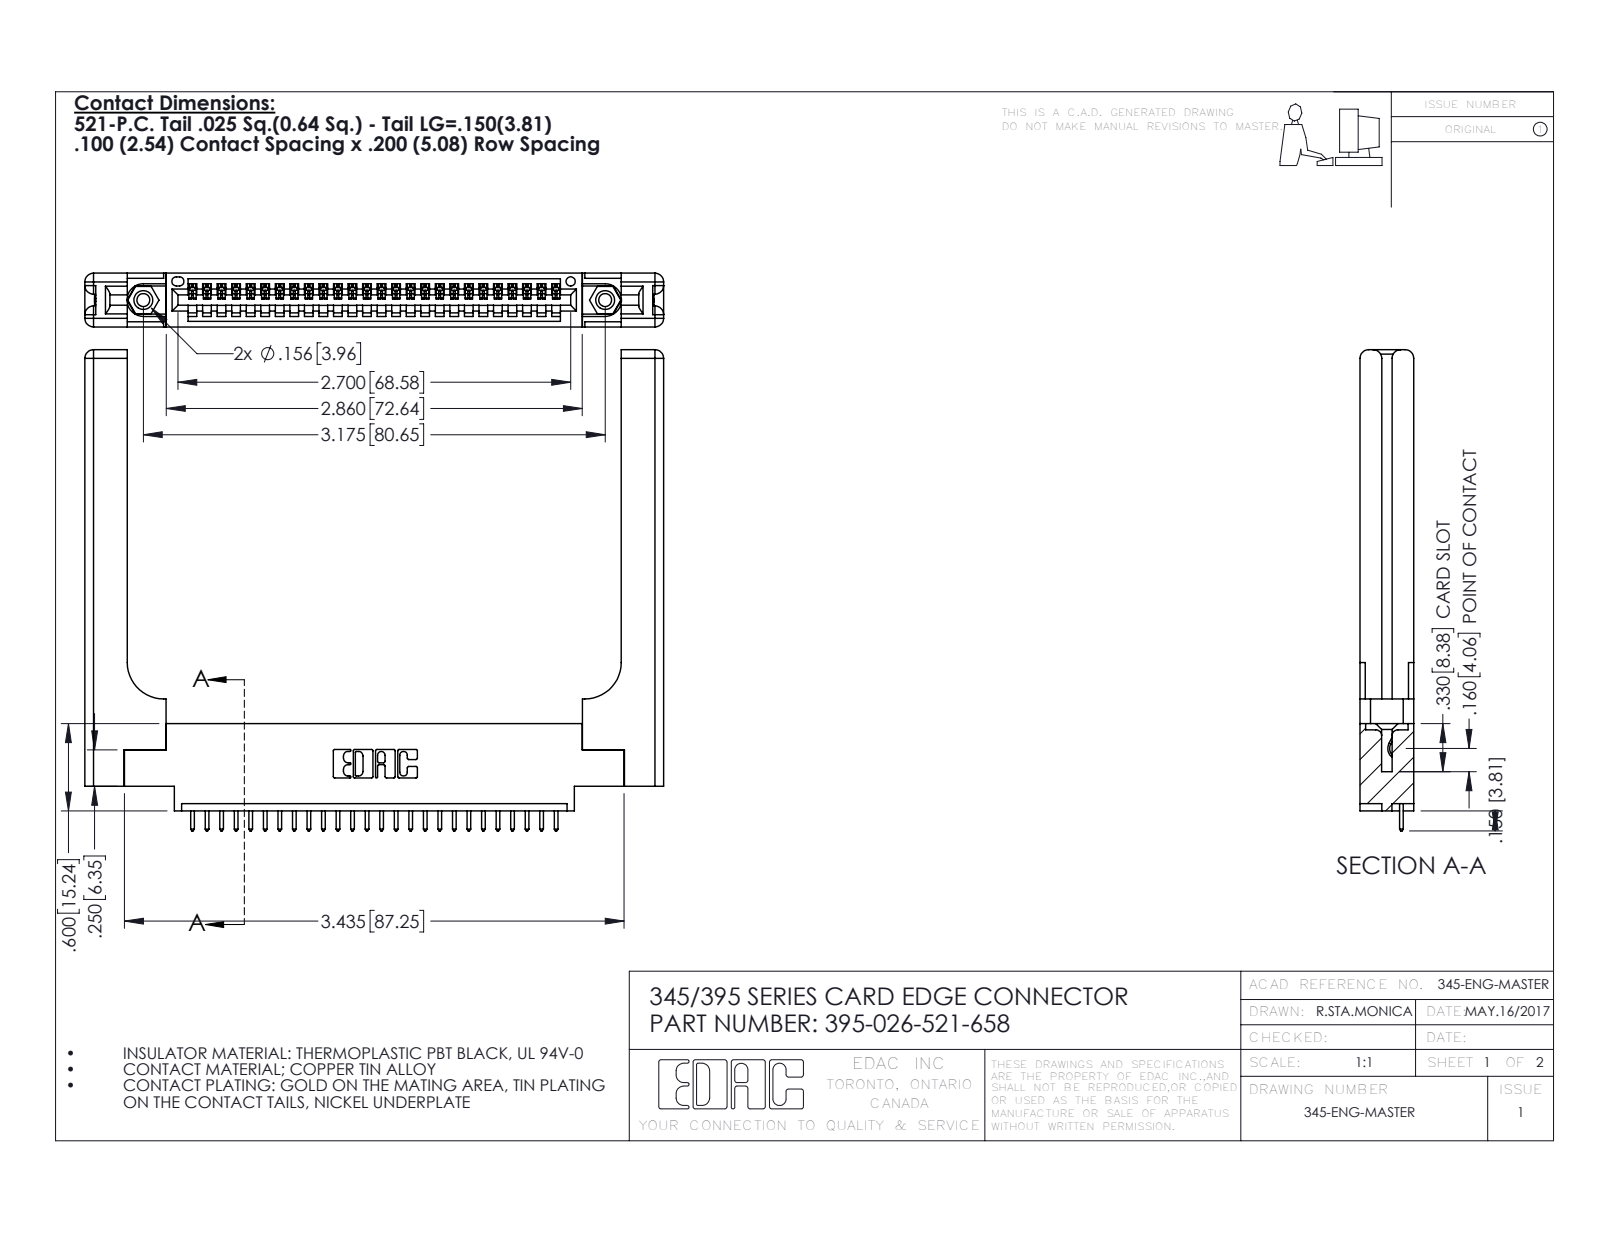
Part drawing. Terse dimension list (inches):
name: 345 Part_0.170 Offset - 0.156 Dia-TH; 345-220-058_345-220-058; 345-250-001_345-250-001-102; 395-026-521-658 (+1 more)
written by: SolidWorks 2016 (CONFIG_CONTROL_DESIGN)
unit: in
bodies: 31 solids, 1894 faces (1272 planar, 562 cylindrical, 60 other)
size: 3.979 × 3.307 × 0.37
volume: 1.085 in³; area: 26.75 in²
holes: 2× ⌀0.089, 2× ⌀0.125, 2× ⌀0.156, 1× ⌀0.064
bosses: 2× ⌀0.155
rounds: 52× R0.006, 52× R0.01, 22× R0.01, 16× R0.06, 6× R0.007, 6× R0.031, 3× R0.026, 2× R0.03
face distances: 0.37, 0.072, 0.298, 0.148, 0.15, 0.077, 0.098, 0.272, 0.025, 0.2
hole spacings: 0.27, 2.94, 3.175
